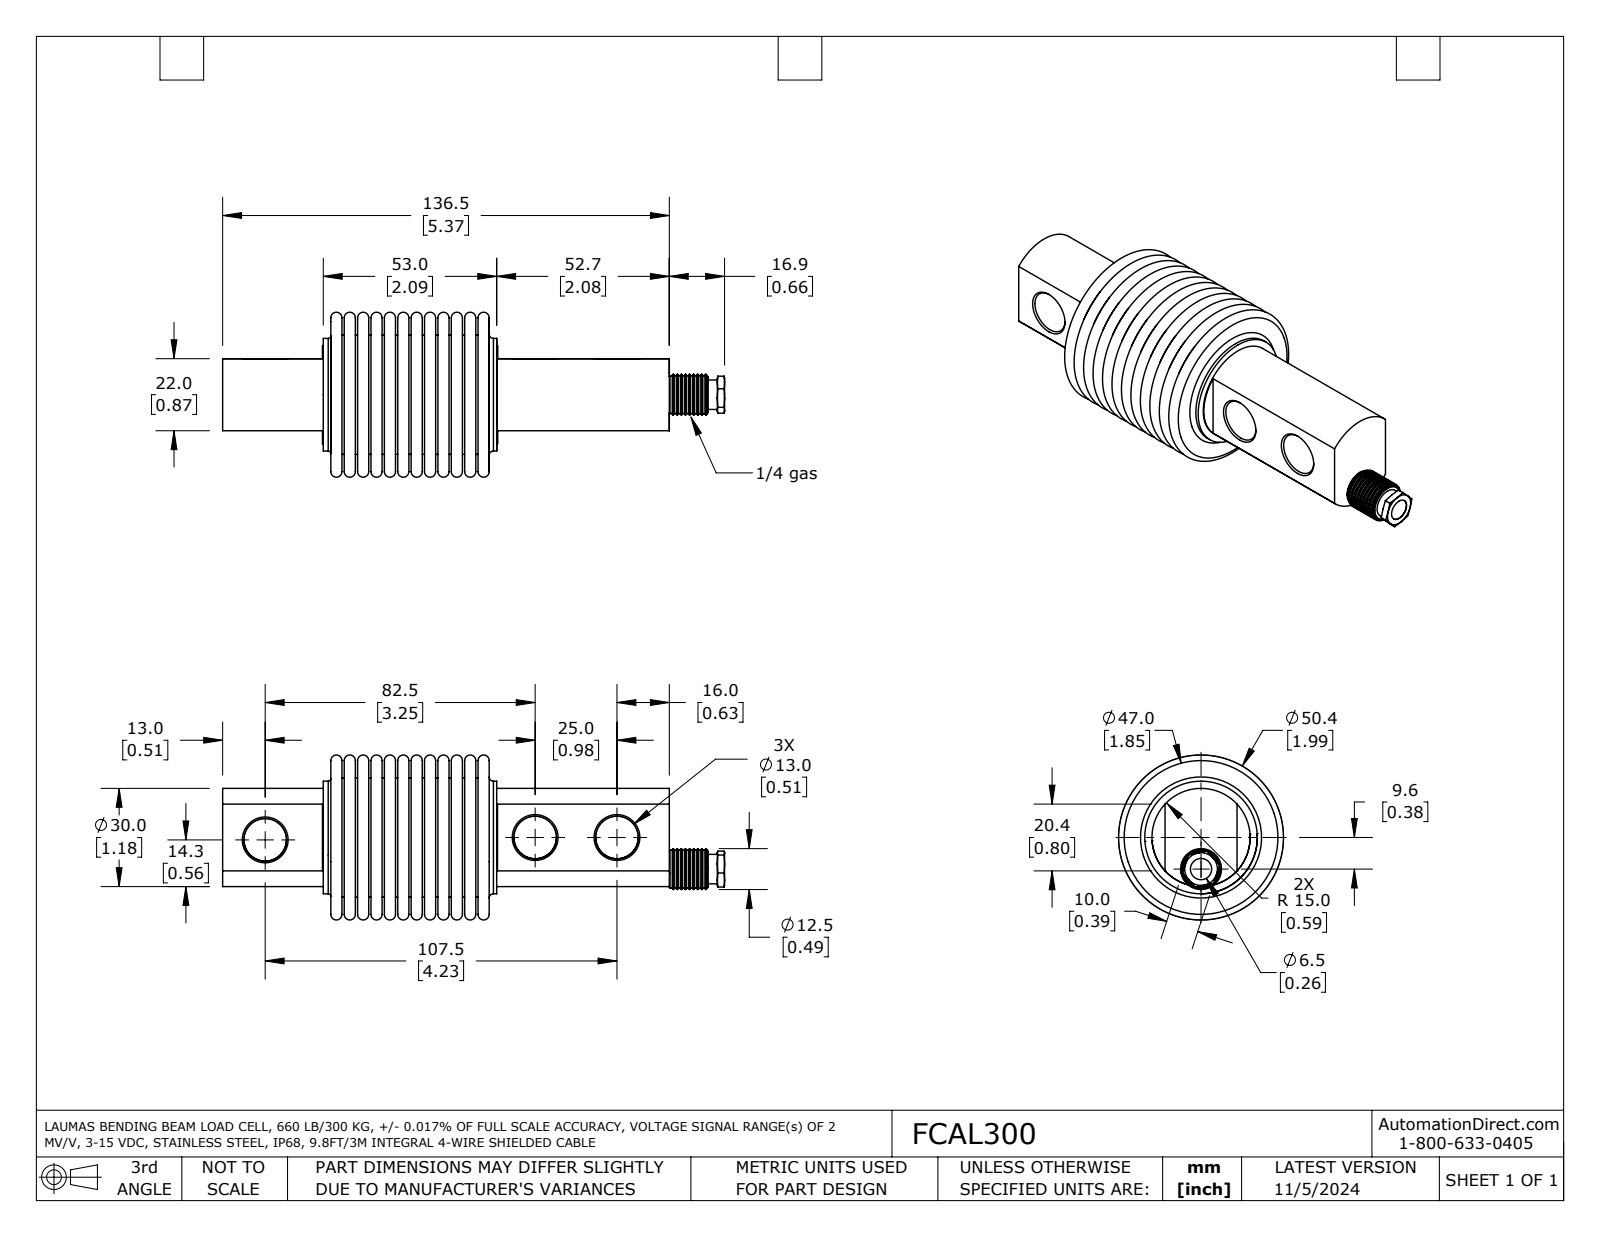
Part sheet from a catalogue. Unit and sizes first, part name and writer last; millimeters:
Units: millimetres
Overall size (bounding box): 153.4 × 50.4 × 50.4
Round holes (diameter × count): ⌀13 ×3, ⌀6.5 ×1, ⌀10 ×1
Round bosses / shafts (diameter × count): ⌀34.4 ×1, ⌀34 ×1, ⌀30 ×1, ⌀11.5 ×1, ⌀9 ×1
Main face-to-face distances: 48.2, 22, 48, 48.4, 103.4, 103.3, 55.2, 55, 33.1, 33.2
Hole centre spacings: 25, 82.5, 107.5
Volume: 86 880 mm³ · Surface area: 75 610 mm²
Bodies: 2 solids, 378 faces (32 planar, 30 cylindrical, 316 other)
Part name (STEP PRODUCT): FCAL300
STEP written by: SolidWorks 2021 (AUTOMOTIVE_DESIGN)
